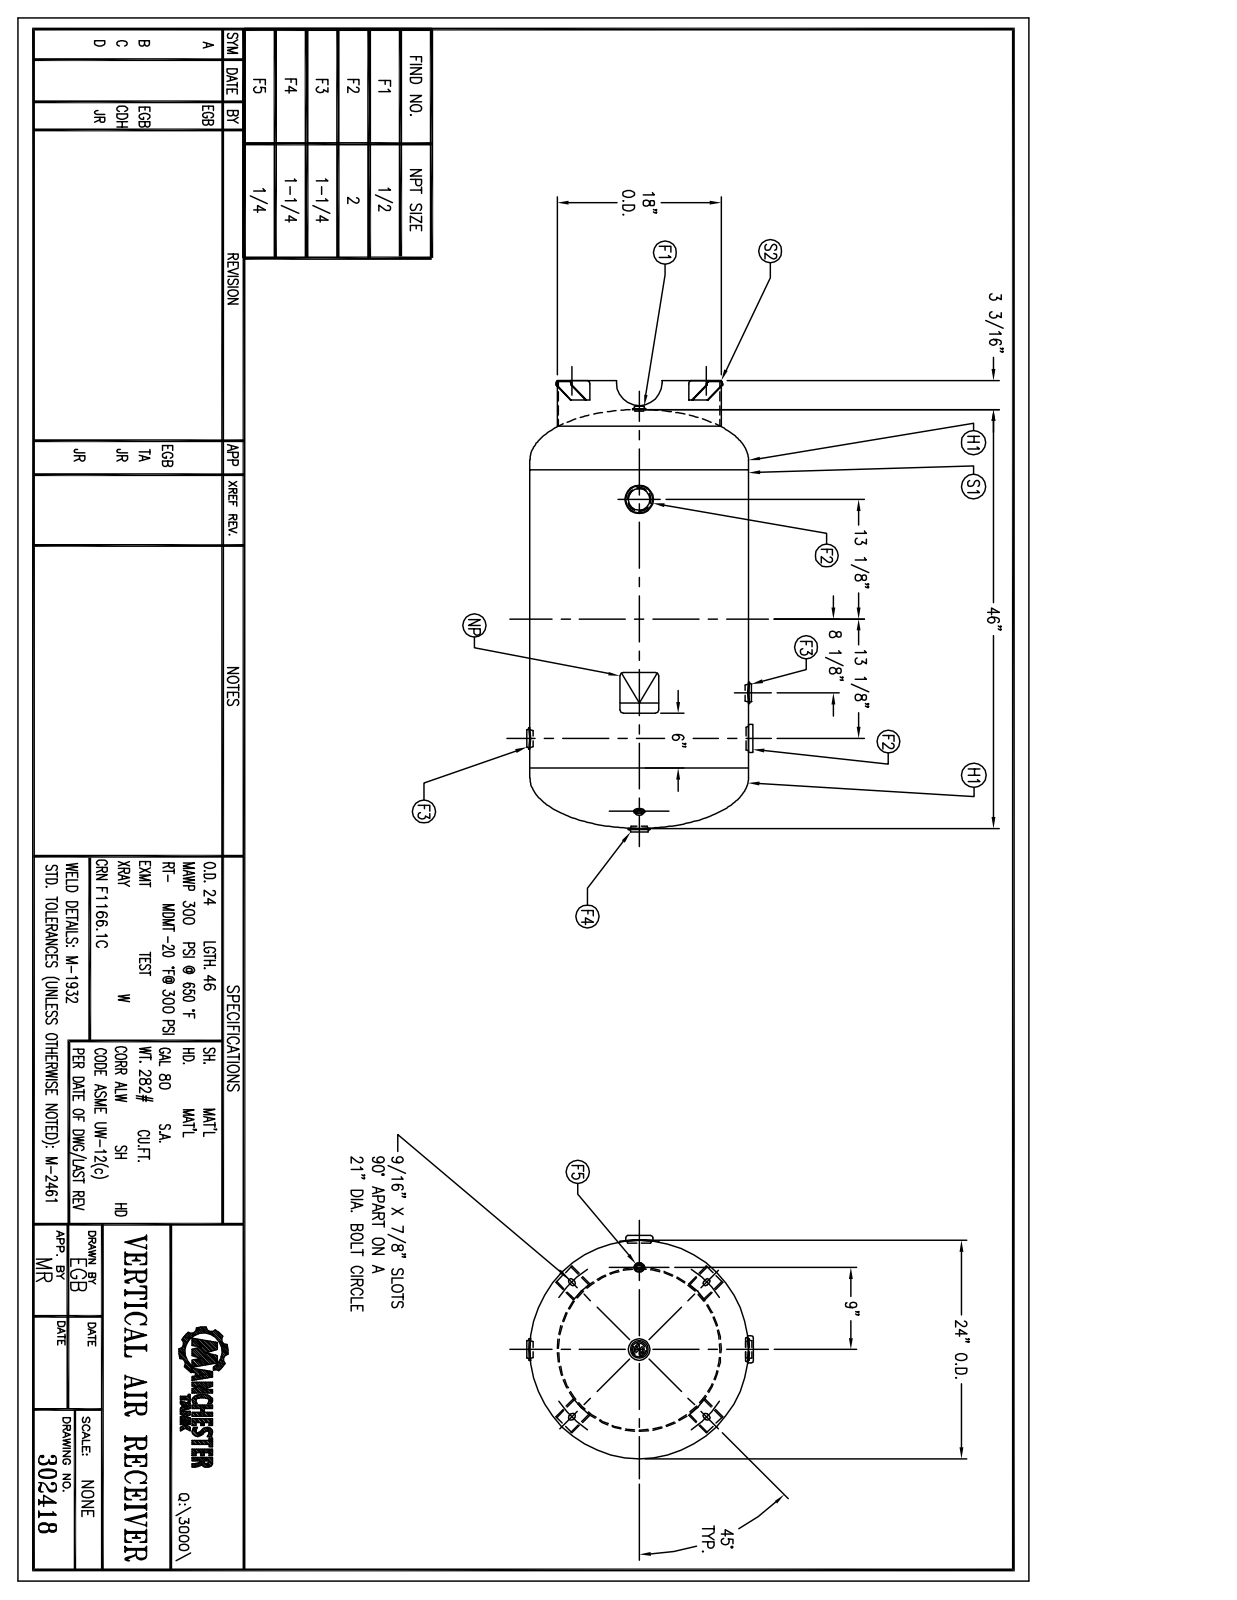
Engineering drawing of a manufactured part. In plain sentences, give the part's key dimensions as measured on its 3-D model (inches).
The part is named "302418". Its 3-D file was written by "SolidWorks 2011 (CONFIG_CONTROL_DESIGN)". It is 0 solids with 240 faces: 89 planar, 73 cylindrical and 78 other. Overall it measures 49.535 by 25.52 by 24.676 inches. Round holes: 3 of diameter 1.66, 2 of diameter 2.375, 1 of diameter 0.54, 1 of diameter 0.84, 1 of diameter 17.732, 1 of diameter 22.75, 1 of diameter 23.456. Round bosses or shafts: 2 of diameter 3, 2 of diameter 2.75, 1 of diameter 24, 1 of diameter 18, 1 of diameter 2.625, 1 of diameter 2.38, 1 of diameter 2.375, 1 of diameter 1.813. Partial cylindrical surfaces (rounded edges, fillets, slot ends): 8 of radius 0.25, 8 of radius 0.281, 8 of radius 0.384, 1 of radius 10.06. The main face-to-face distances are 0.134, 0.063, 2.446, 10.346, 31.5, 41.846, 41.713, 10.213, 2.509, 2.58. The hole center spacings are 5.
